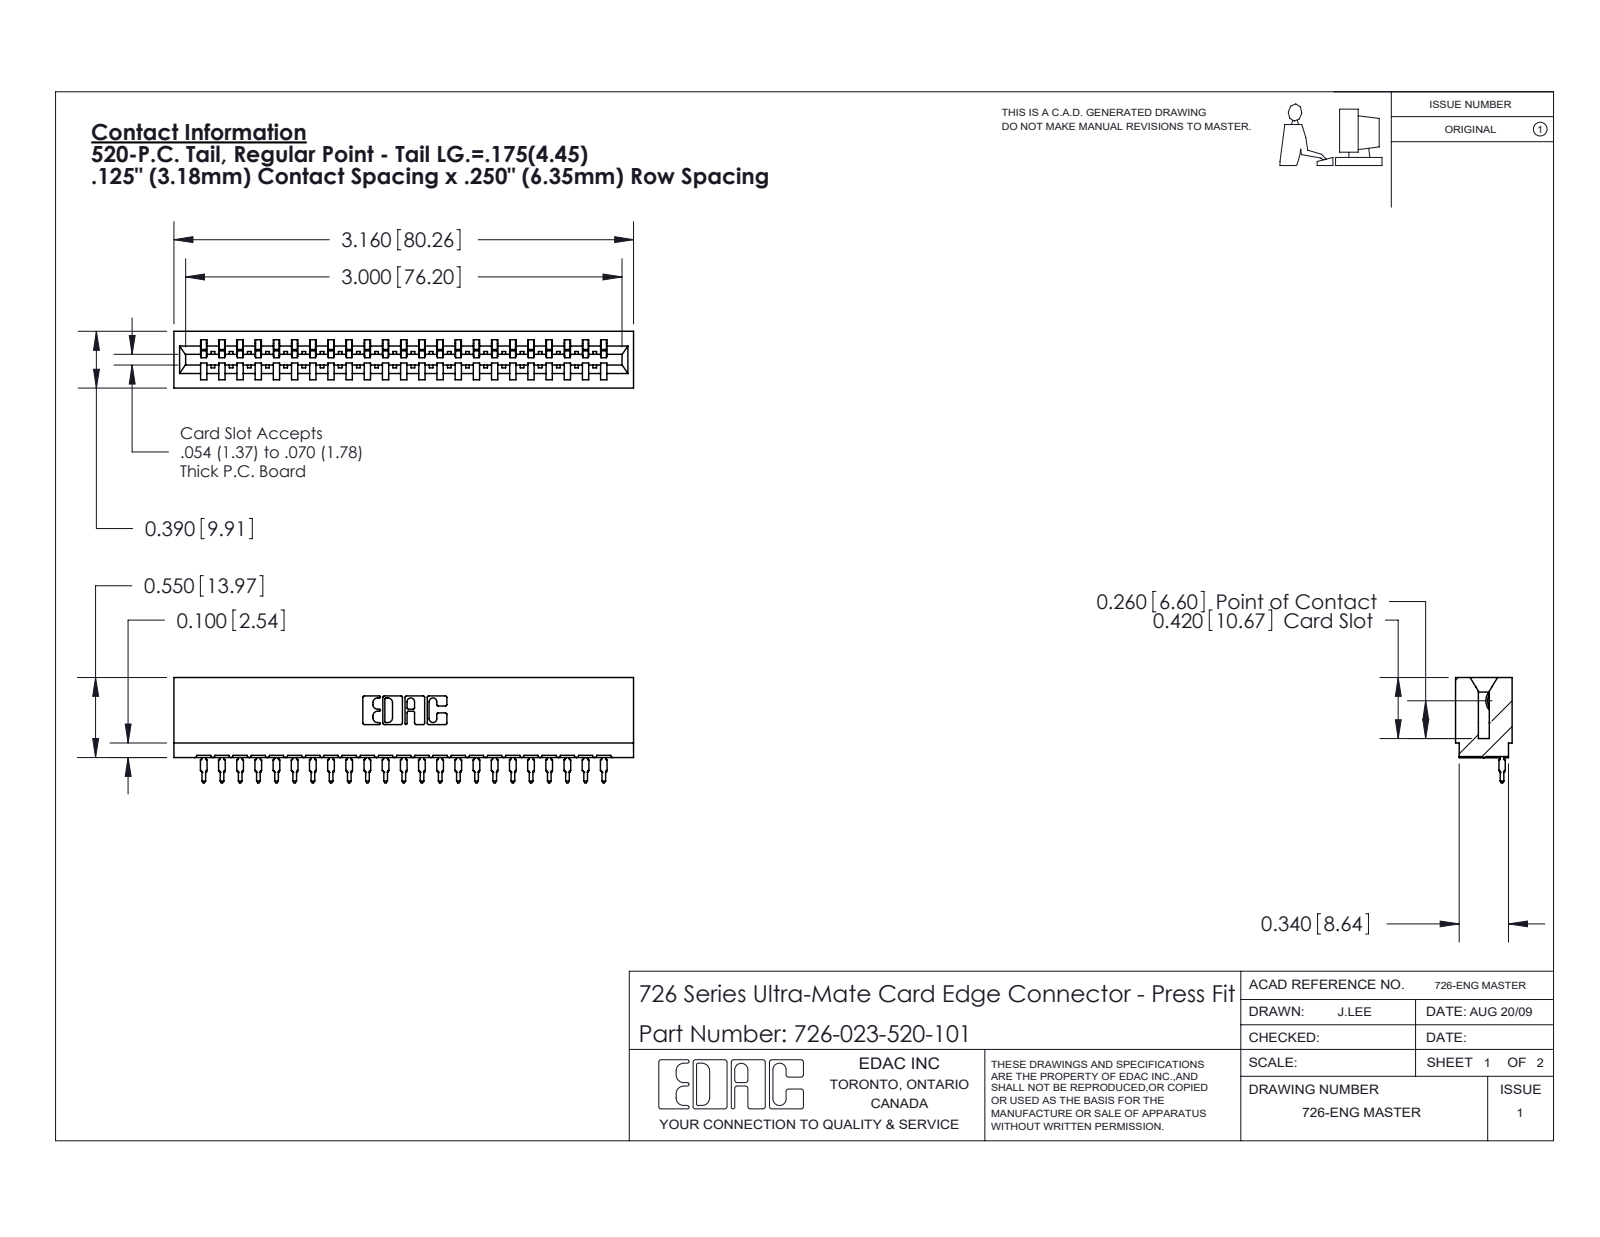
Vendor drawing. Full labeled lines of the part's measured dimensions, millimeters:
Part name (STEP PRODUCT): 726 Part_.515 Slot Depth - 01; 726-023-520-101; 746-292-001_520
STEP written by: SolidWorks 2020 (CONFIG_CONTROL_DESIGN)
Units: millimetres
Bodies: 24 solids, 2581 faces (1504 planar, 479 cylindrical, 598 other)
Overall size (bounding box): 80.3 × 18.4 × 9.9
Volume: 7 240 mm³ · Surface area: 10 610 mm²
Partial cylindrical surfaces — rounded edges, fillets, slot ends (radius × count): R0.5 ×46, R0.4 ×24, R0.3 ×22, R0.2 ×6, R0.8 ×6, R0.1 ×4, R0.3 ×4, R0.7 ×3
Main face-to-face distances: 1.4, 8.5, 9.9, 0.6, 7.8, 19.1, 1.1, 12.7, 3.2, 6.4
